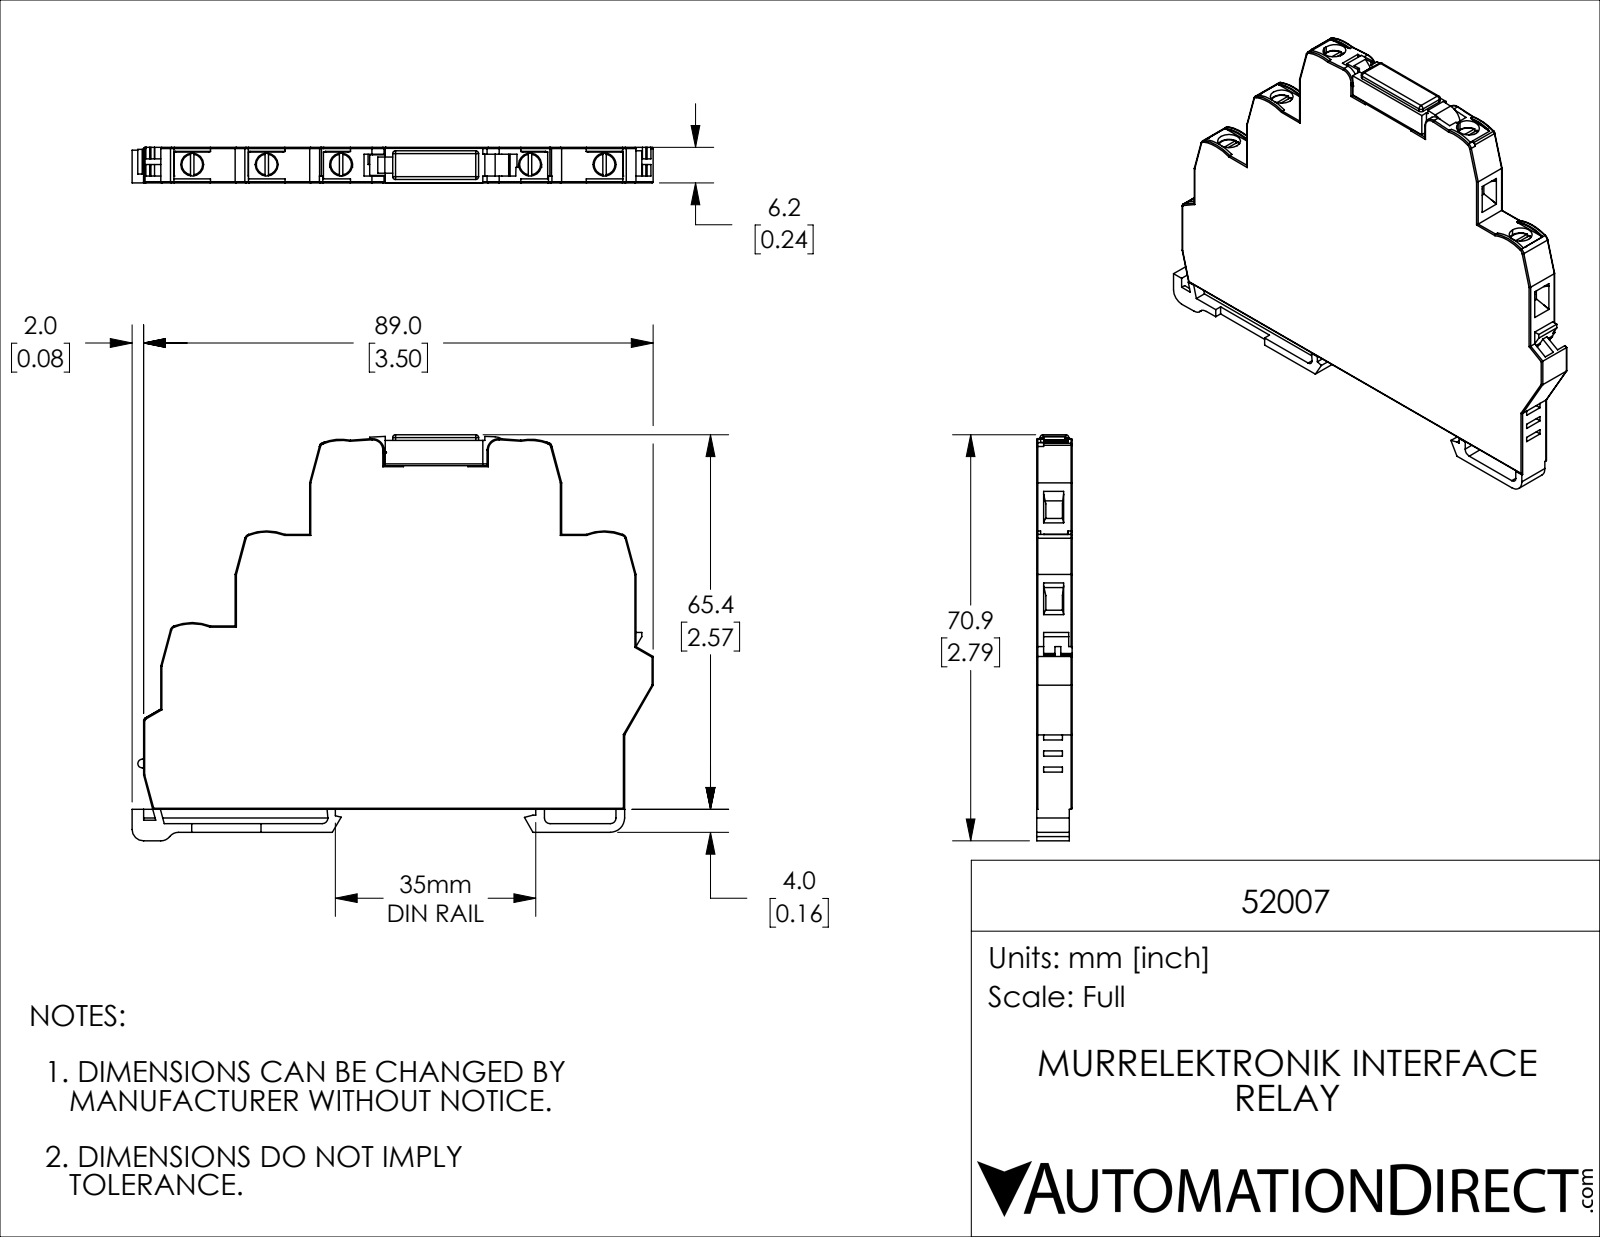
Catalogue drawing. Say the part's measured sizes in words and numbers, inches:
The part is named "52007". Its 3-D file was written by "SolidWorks 2019 (CONFIG_CONTROL_DESIGN)". It is 2 solids with 566 faces: 351 planar, 147 cylindrical and 68 other. Overall it measures 3.583 by 2.791 by 0.244 inches. Its volume is 1.706 cubic inches and its surface area 20.13 square inches. Round holes: 5 of diameter 0.157, 1 of diameter 0.075. Round bosses or shafts: 1 of diameter 0.079. Partial cylindrical surfaces (rounded edges, fillets, slot ends): 56 of radius 0.008, 11 of radius 0.02, 8 of radius 0.039, 6 of radius 0.079, 5 of radius 0.03, 5 of radius 0.346, 4 of radius 0.005, 3 of radius 0.016. The main face-to-face distances are 0.244, 0.059, 0.197, 0.098, 0.157, 0.118, 0.047, 0.02, 0.039, 2.362. The hole center spacings are 0.512, 1.811, 2.323, 1.024, 1.299, 2.835.
